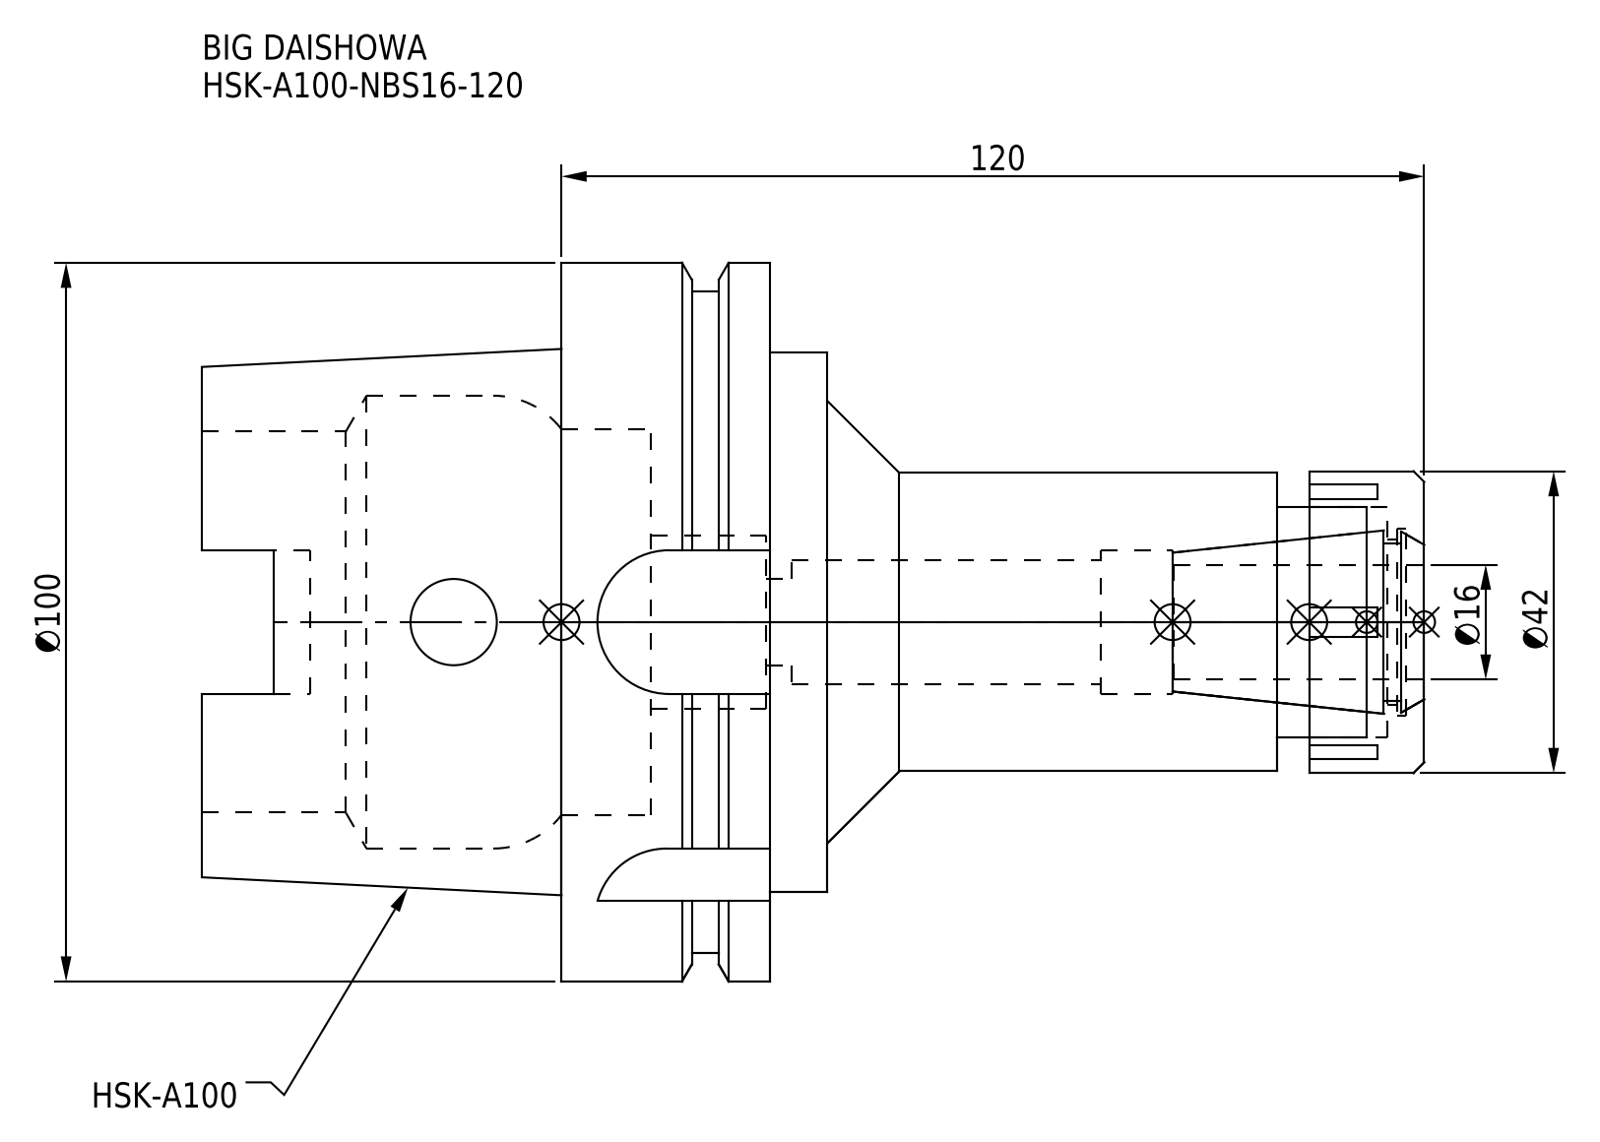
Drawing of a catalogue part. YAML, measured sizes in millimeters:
part_name: "HSK-A100-NBS16-120_1.stp; NBN16_1.stp; HA100NB16120-160_ASM.stp; HSK-A100-NBS16-120 (+3 more)"
step_written_by: "SolidWorks 2019 (CONFIG_CONTROL_DESIGN)"
units: millimeters
bodies: {solids: 2, faces: 138, planar: 66, cylindrical: 50, other: 22}
overall_size: [170, 100, 100]
volume: 377509
surface_area: 71201
round_holes:
  - {diameter: 12, count: 2}
  - {diameter: 17.3, count: 1}
  - {diameter: 20, count: 1}
  - {diameter: 23, count: 1}
  - {diameter: 24, count: 1}
  - {diameter: 26, count: 1}
  - {diameter: 32, count: 1}
  - {diameter: 53, count: 1}
  - {diameter: 53.8, count: 1}
  - {diameter: 63, count: 1}
round_bosses_or_shafts:
  - {diameter: 100, count: 1}
  - {diameter: 92, count: 1}
  - {diameter: 75, count: 1}
  - {diameter: 42, count: 1}
  - {diameter: 41.5, count: 1}
partial_cylinders:
  - {radius: 4.88, count: 4}
  - {radius: 10, count: 4}
face_to_face_distances: [29, 8, 16.55, 12.45, 37, 24.55, 83, 50, 87, 79]
